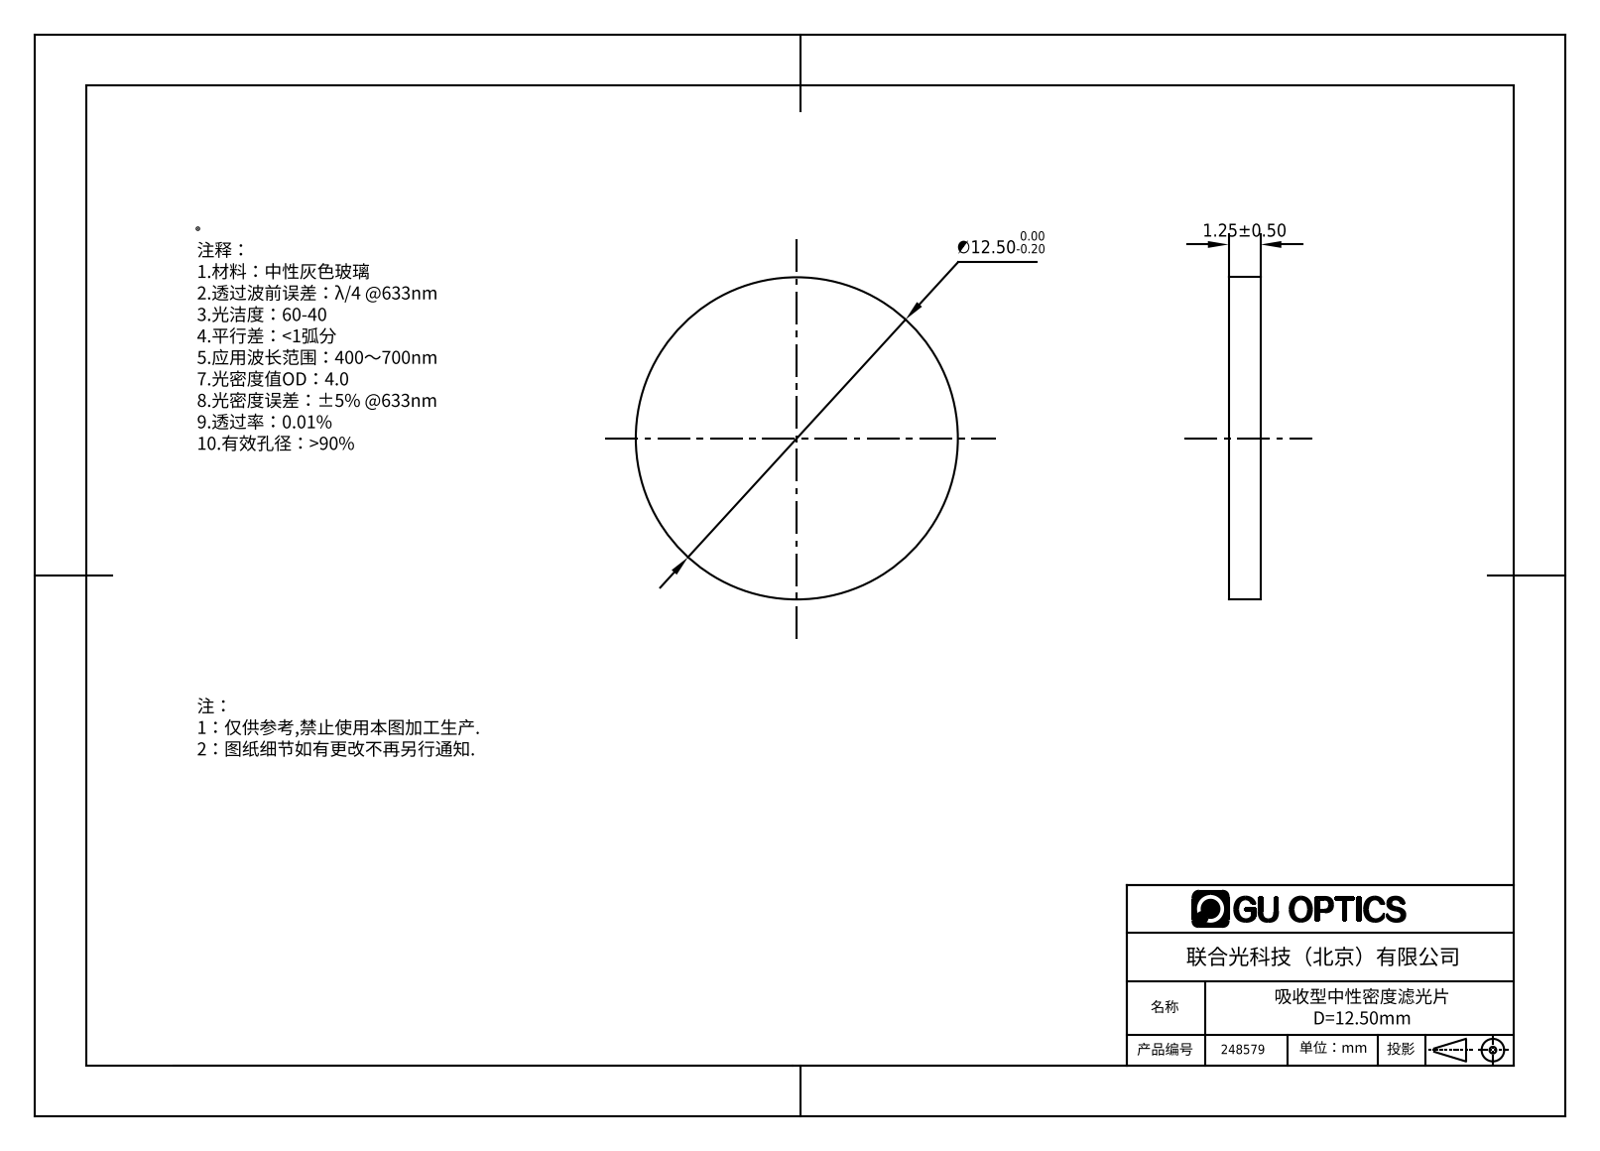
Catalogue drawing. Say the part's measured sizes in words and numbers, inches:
The part is named "248579". Its 3-D file was written by "SolidWorks 2016 (AUTOMOTIVE_DESIGN)". It is 1 solid with 4 faces: 2 planar, 2 cylindrical and 0 other. Overall it measures 0.492 by 0.492 by 0.049 inches. Its volume is 0.009 cubic inches and its surface area 0.457 square inches. Round bosses or shafts: 1 of diameter 0.492. The main face-to-face distances are 0.049.
